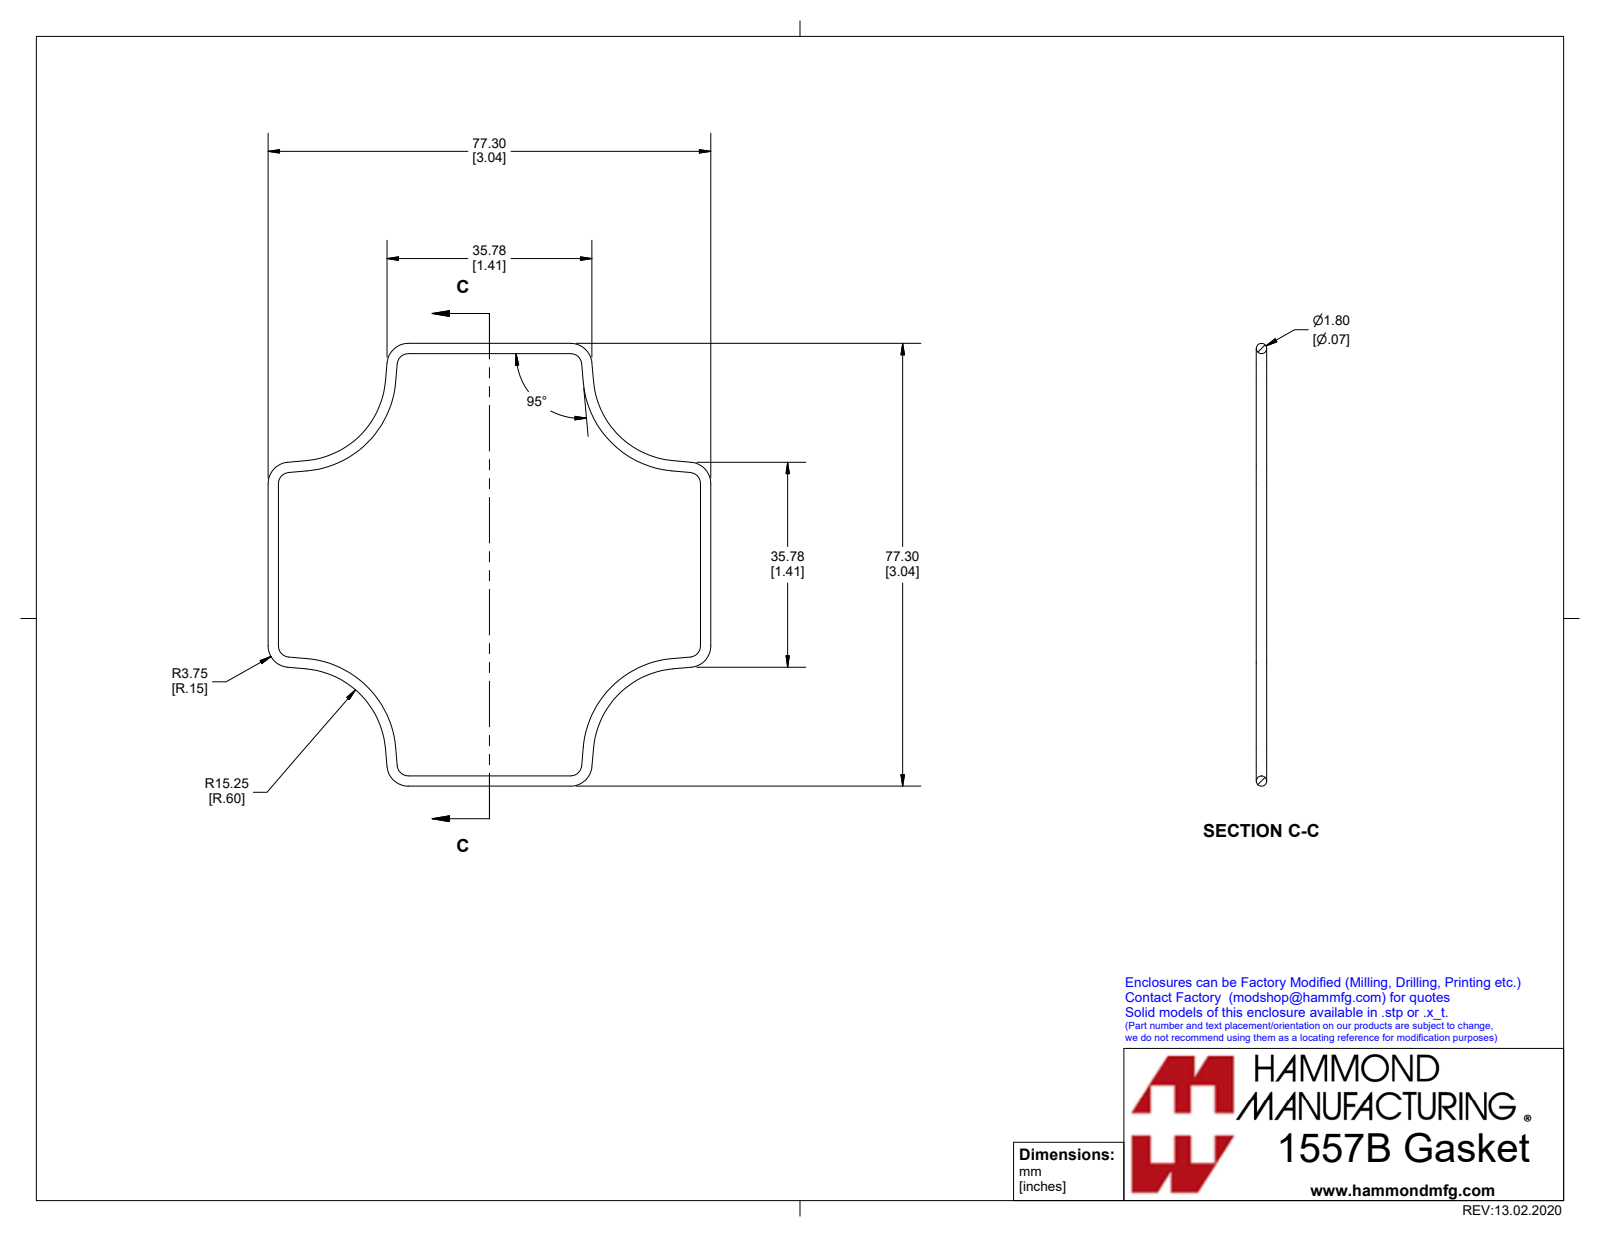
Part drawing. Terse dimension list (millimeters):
name: 1557BGASKET
written by: SolidWorks 2019 (AUTOMOTIVE_DESIGN)
unit: mm
bodies: 1 solid, 146 faces (26 planar, 56 cylindrical, 64 other)
size: 77.3 × 77.3 × 1.8
volume: 707 mm³; area: 1 532 mm²
rounds: 48× R0.8, 4× R15.25, 4× R17.05
face distances: 1.8, 75.5, 73.7, 77.3, 40.04, 38.24, 41.84
